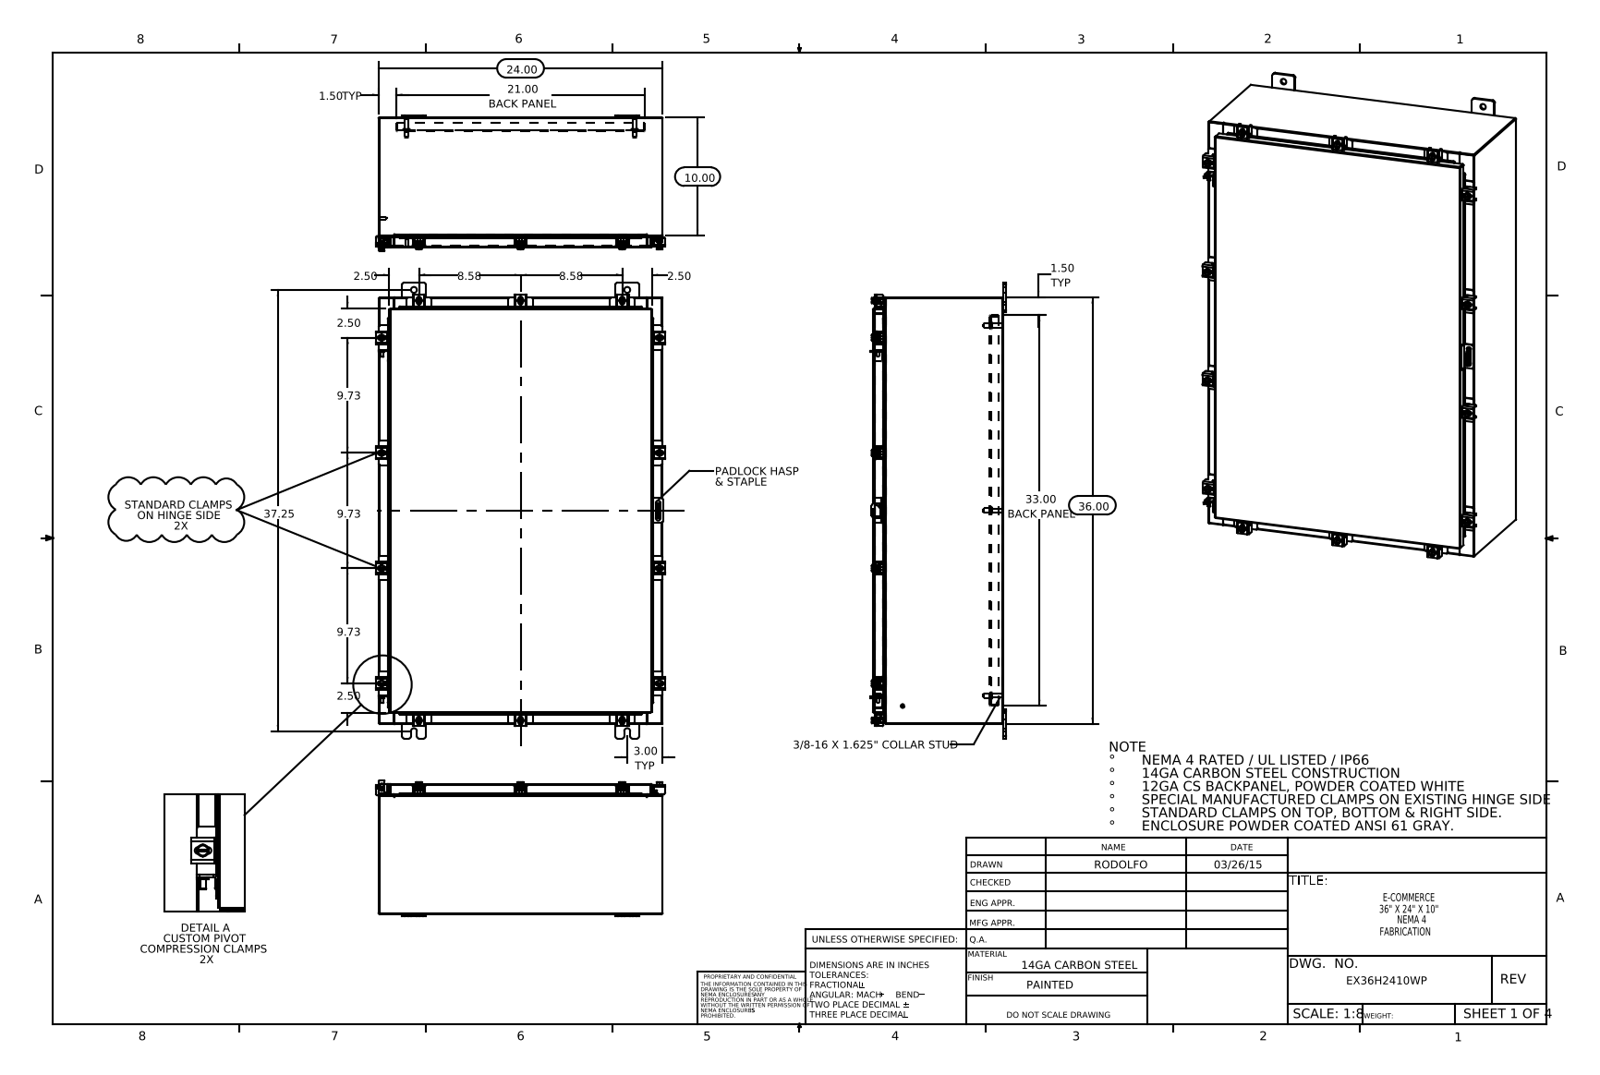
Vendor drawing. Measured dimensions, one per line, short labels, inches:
name: EX36H2410WP Clamp Bracket; EX36H2410WP Mounting Studs; N-WMT04X30402202210-00 22104005_DEFAULT; N-WMT04X30402202210-00 22101002 (+8 more)
written by: SolidWorks 2014 (CONFIG_CONTROL_DESIGN)
unit: in
bodies: 93 solids, 2322 faces (1221 planar, 905 cylindrical, 196 other)
size: 38.5 × 24.421 × 11.453
volume: 327.4 in³; area: 8 148 in²
holes: 14× ⌀0.213, 14× ⌀0.26, 10× ⌀0.5, 1× ⌀0.125, 1× ⌀0.25
bosses: 14× ⌀0.5, 14× ⌀0.25, 12× ⌀0.399, 6× ⌀0.625, 6× ⌀0.375, 6× ⌀0.33, 2× ⌀0.315, 2× ⌀0.236
rounds: 62× R0.06, 28× R0.141, 26× R0.013, 26× R0.12, 24× R0.19, 22× R0.088, 20× R0.09, 19× R0.05
face distances: 0.075, 10.9, 10.975, 10.826, 0.104, 23.925, 1, 1.075, 9.826, 9.9
hole spacings: 25.389, 2.347, 4.44, 5.299, 9.73, 10.964, 13.241, 14.744
